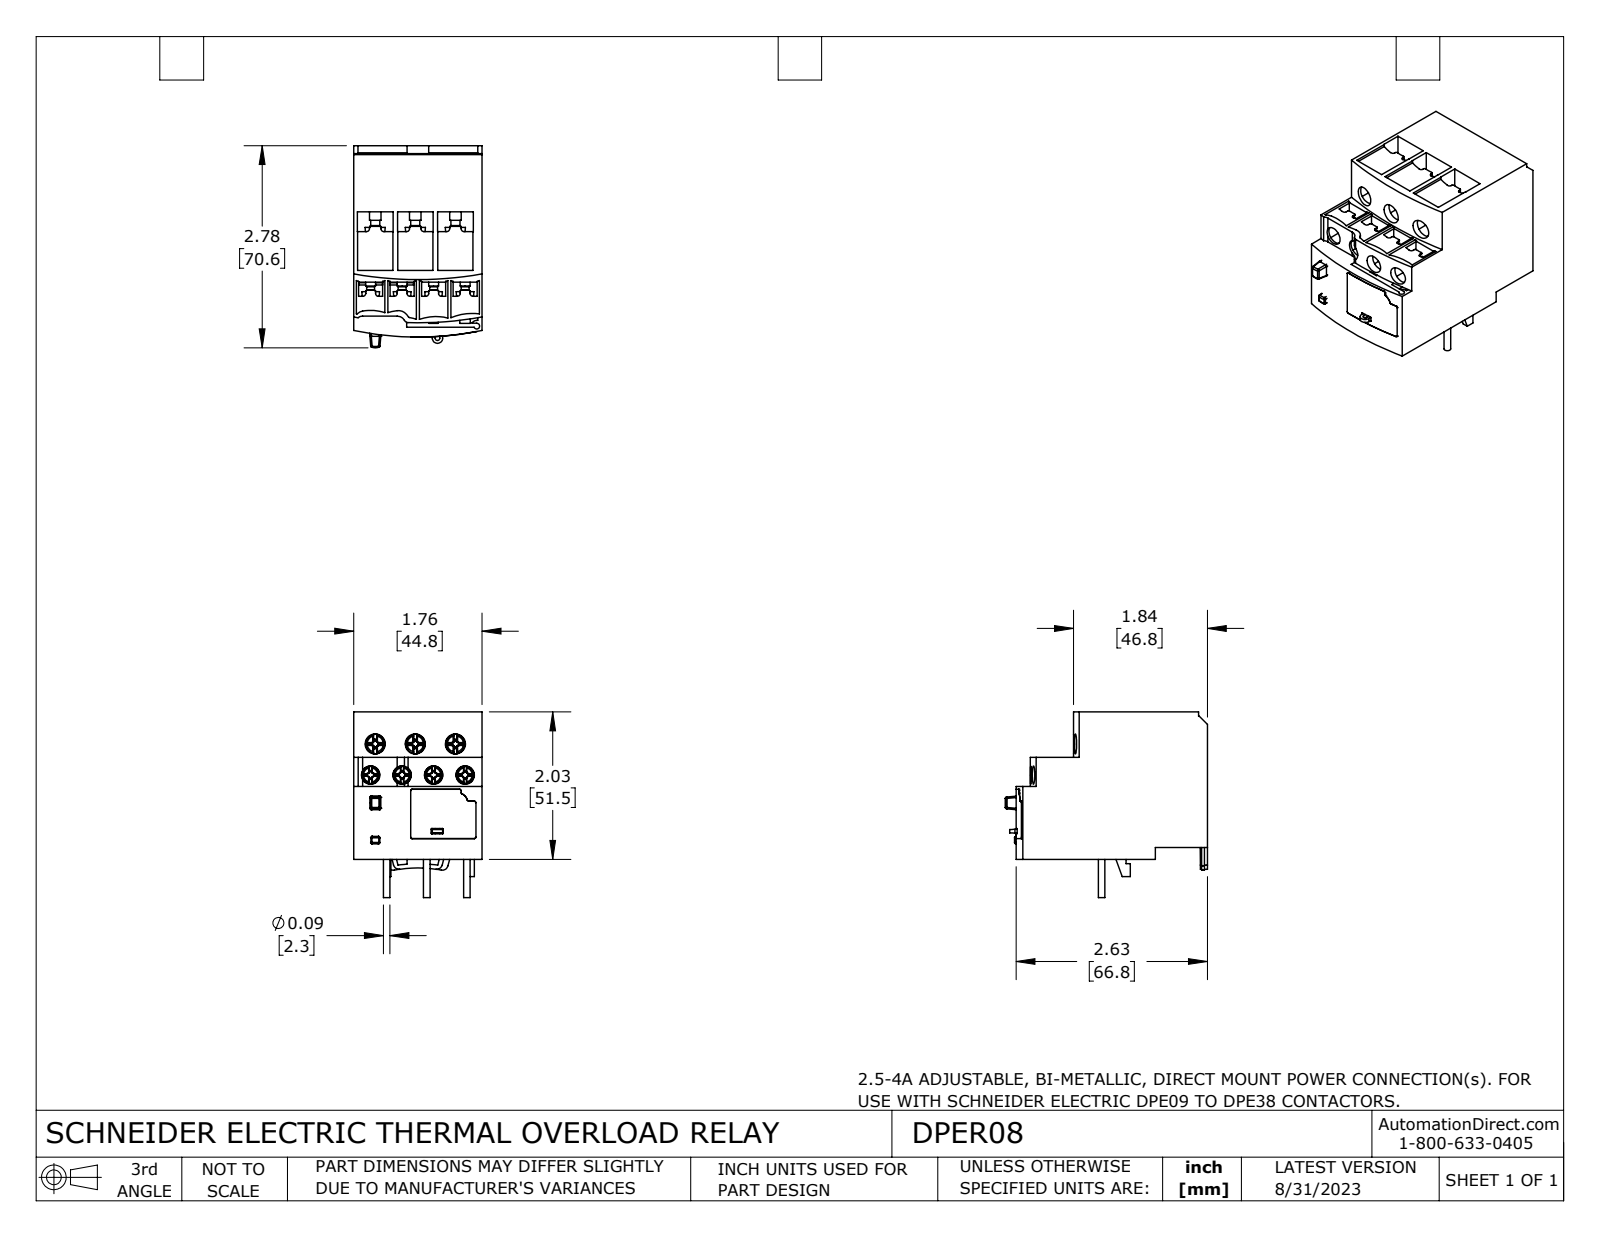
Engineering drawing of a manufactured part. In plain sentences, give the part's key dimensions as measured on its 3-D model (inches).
The part is named "DPER08". Its 3-D file was written by "SolidWorks 2021 (CONFIG_CONTROL_DESIGN)". It is 16 solids with 1212 faces: 676 planar, 269 cylindrical and 267 other. Overall it measures 2.778 by 2.553 by 1.764 inches. Its volume is 6.953 cubic inches and its surface area 47.15 square inches. Round holes: 4 of diameter 0.252, 3 of diameter 0.276, 2 of diameter 0.079, 2 of diameter 0.118, 1 of diameter 0.059, 1 of diameter 0.244. Round bosses or shafts: 12 of diameter 0.091, 4 of diameter 0.138, 4 of diameter 0.108, 3 of diameter 0.157, 3 of diameter 0.154, 3 of diameter 0.124, 1 of diameter 0.118, 1 of diameter 0.107. Partial cylindrical surfaces (rounded edges, fillets, slot ends): 52 of radius 0.02, 22 of radius 0.039, 19 of radius 0.004, 8 of radius 0.012, 6 of radius 0.008, 6 of radius 0.63, 4 of radius 0.079, 2 of radius 0.024. The main face-to-face distances are 1.764, 0.165, 2.028, 1.863, 0.909, 0.551, 0.618, 1.409, 1.245, 2.497. The hole center spacings are 0.433, 0.551, 0.866, 0.334, 0.381, 0.404, 0.422, 0.449.
